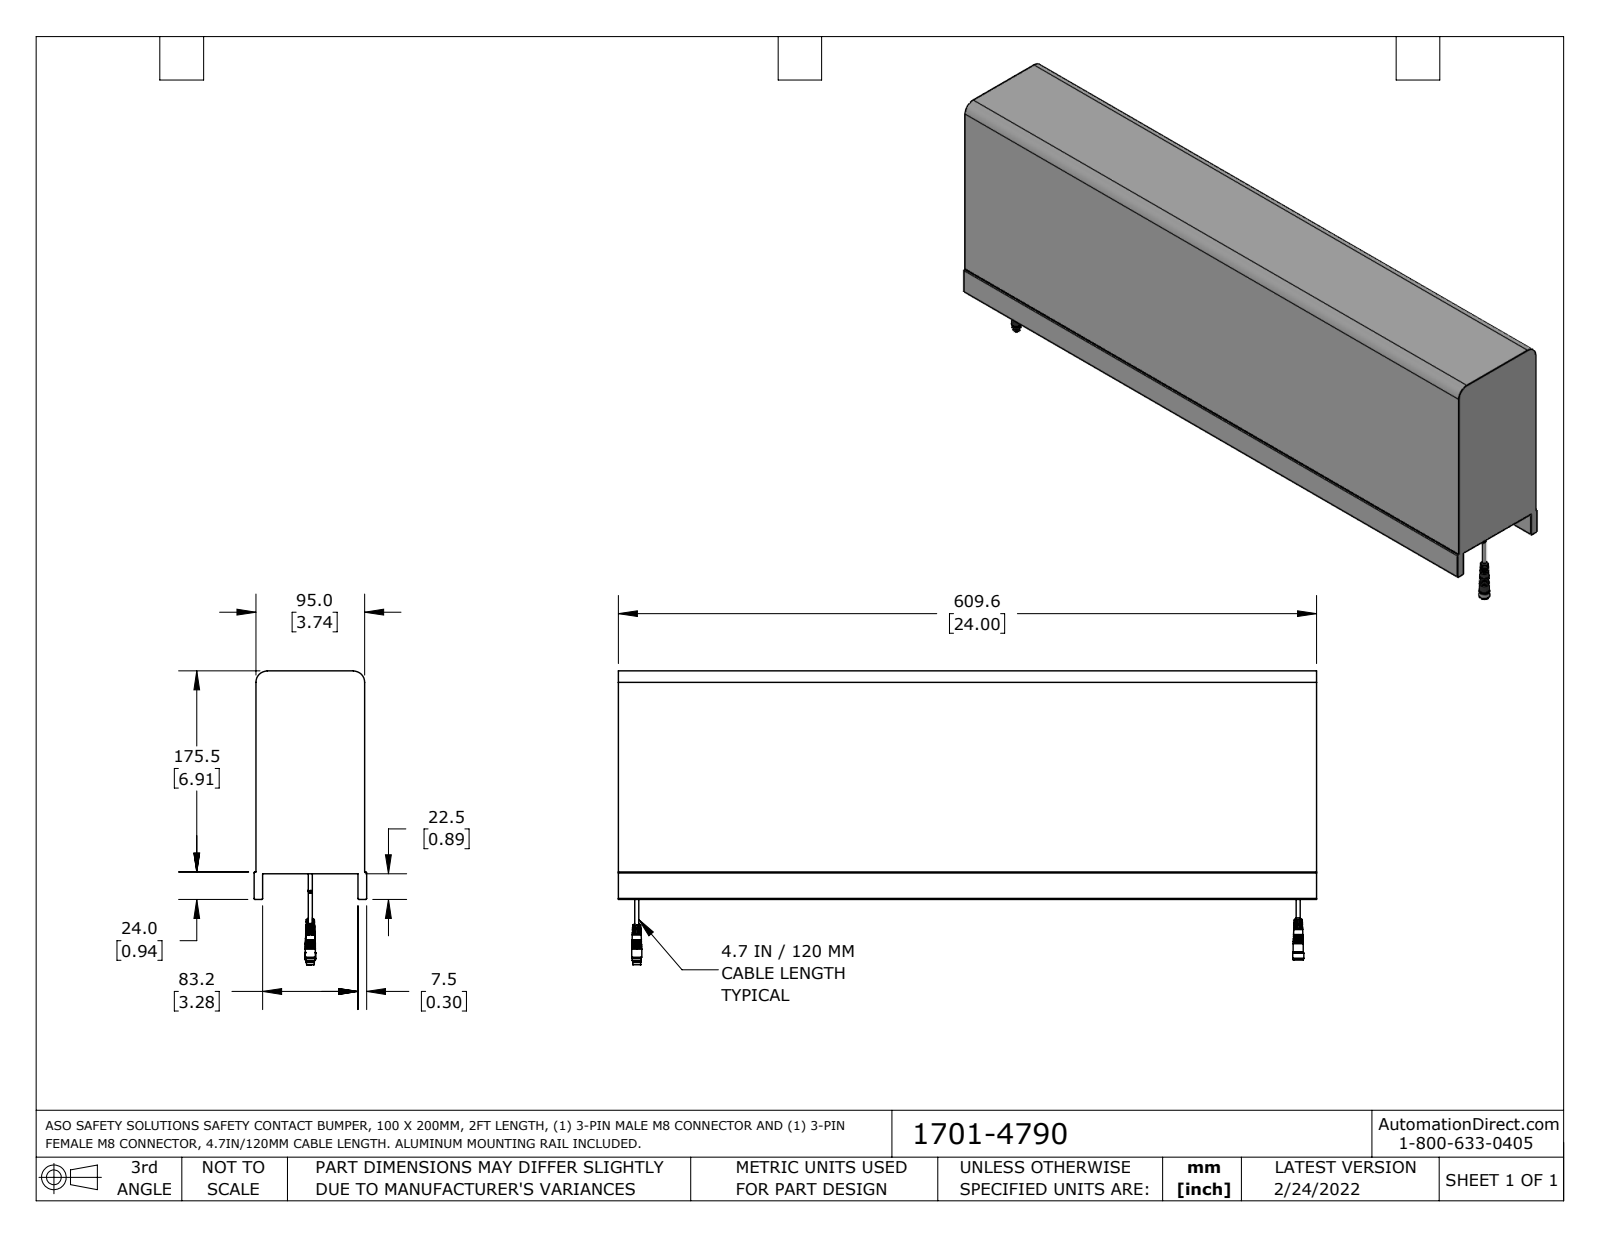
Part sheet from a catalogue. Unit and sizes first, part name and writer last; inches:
Units: inches
Overall size (bounding box): 24 × 10.096 × 3.868
Round holes (diameter × count): ⌀0.047 ×4, ⌀0.033 ×3, ⌀0.063 ×3, ⌀0.134 ×2, ⌀0.228 ×1, ⌀0.232 ×1, ⌀0.272 ×1, ⌀0.283 ×1
Round bosses / shafts (diameter × count): ⌀0.047 ×8, ⌀0.039 ×6, ⌀0.02 ×4, ⌀0.346 ×2, ⌀0.224 ×2, ⌀0.138 ×2, ⌀0.378 ×1, ⌀0.354 ×1
Partial cylindrical surfaces — rounded edges, fillets, slot ends (radius × count): R0.039 ×4, R0.03 ×2, R0.394 ×2
Main face-to-face distances: 3.74, 6.969, 0.064, 3.804, 0.295, 3.572, 0.231, 3.509, 24, 3.868
Hole centre spacings: 22.74, 0.028, 0.069, 22.671, 22.713, 22.768, 22.809, 0.041
Volume: 636.9 in³ · Surface area: 658.5 in²
Bodies: 24 solids, 447 faces (175 planar, 154 cylindrical, 118 other)
Part name (STEP PRODUCT): 1701-4790_Default
STEP written by: SolidWorks 2021 (CONFIG_CONTROL_DESIGN)
